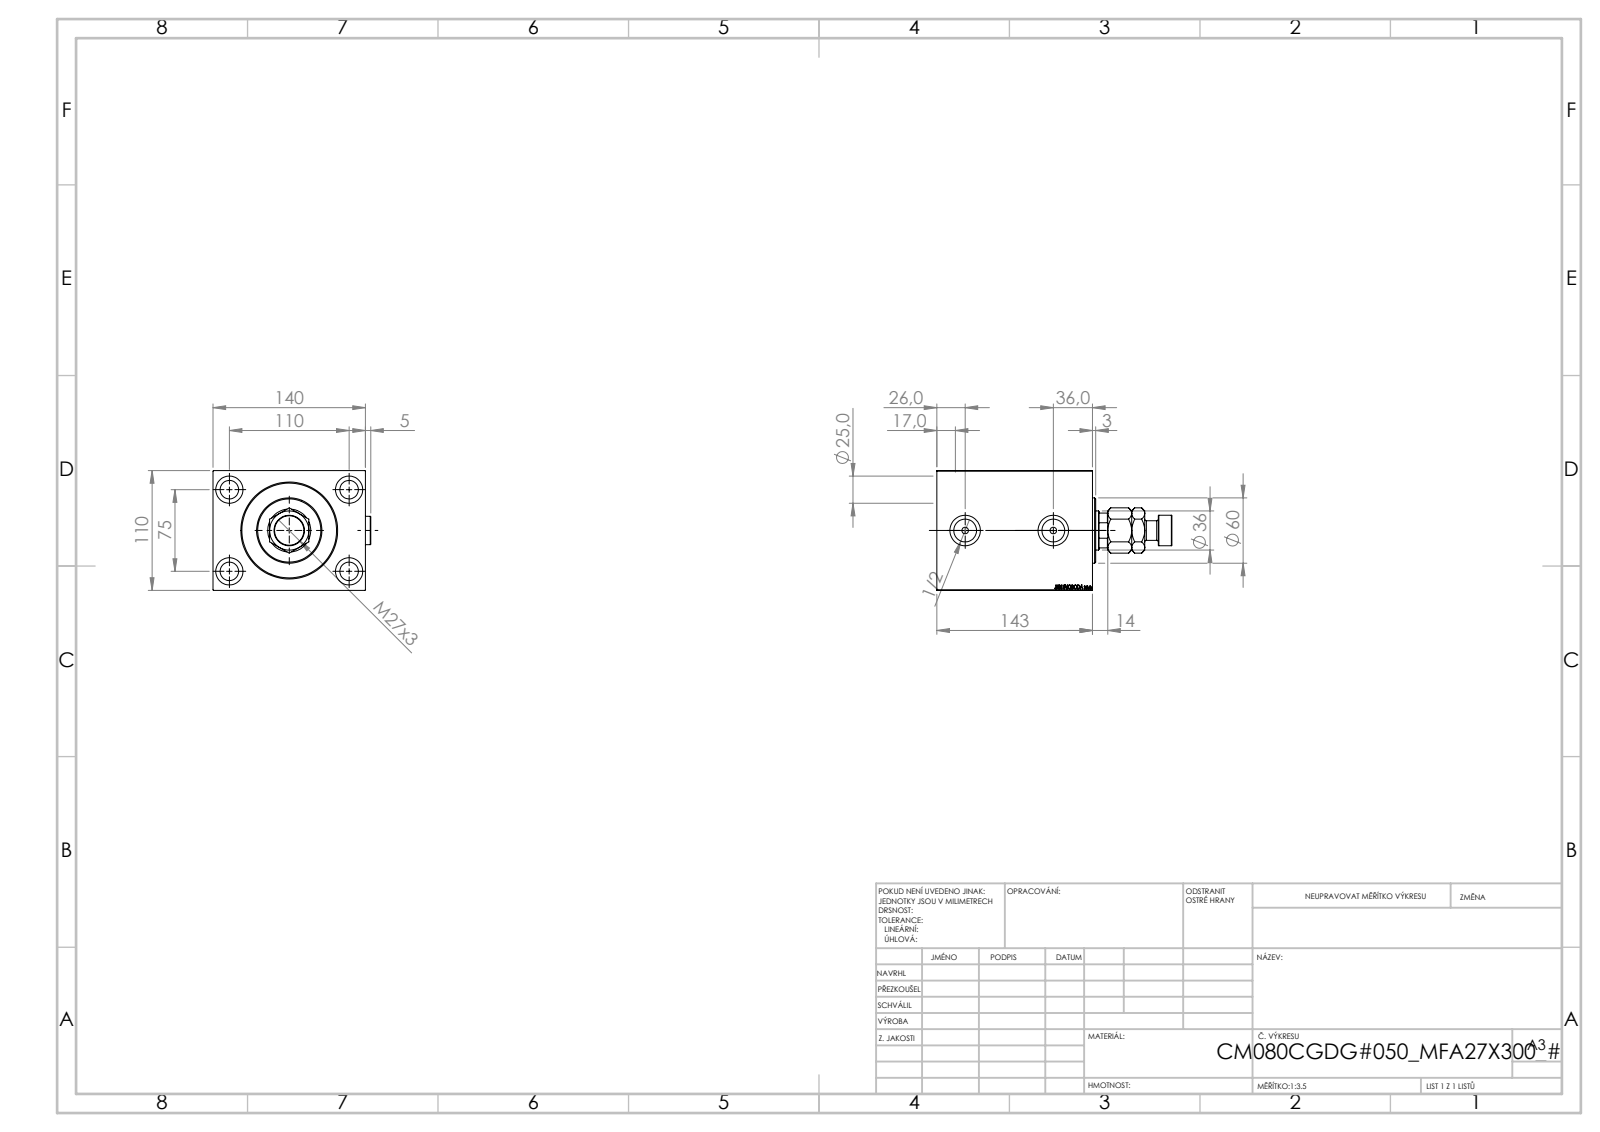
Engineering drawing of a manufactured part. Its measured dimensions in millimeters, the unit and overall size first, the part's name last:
Units: millimetres
Overall size (bounding box): 216 × 144.9 × 110
Round holes (diameter × count): ⌀17 ×4, ⌀25 ×4, ⌀6 ×2, ⌀20.96 ×2, ⌀28 ×2, ⌀25.5 ×1, ⌀36 ×1, ⌀39.5 ×1, ⌀80 ×1, ⌀82 ×1, ⌀87 ×1
Round bosses / shafts (diameter × count): ⌀26 ×2, ⌀60 ×1, ⌀28 ×1, ⌀18 ×1
Partial cylindrical surfaces — rounded edges, fillets, slot ends (radius × count): R17.5 ×1
Main face-to-face distances: 110, 140, 143, 122, 21, 14, 129, 108, 64, 50
Hole centre spacings: 66.57, 75, 110, 133.14, 81
Volume: 1 870 000 mm³ · Surface area: 233 408 mm²
Bodies: 6 solids, 971 faces (459 planar, 82 cylindrical, 430 other)
Part name (STEP PRODUCT): Zatka_OIL_PORT; V450CM_C_Body; V450CM_C_VCP; MFA (+1 more)
STEP written by: SolidWorks 2019 (CONFIG_CONTROL_DESIGN)
